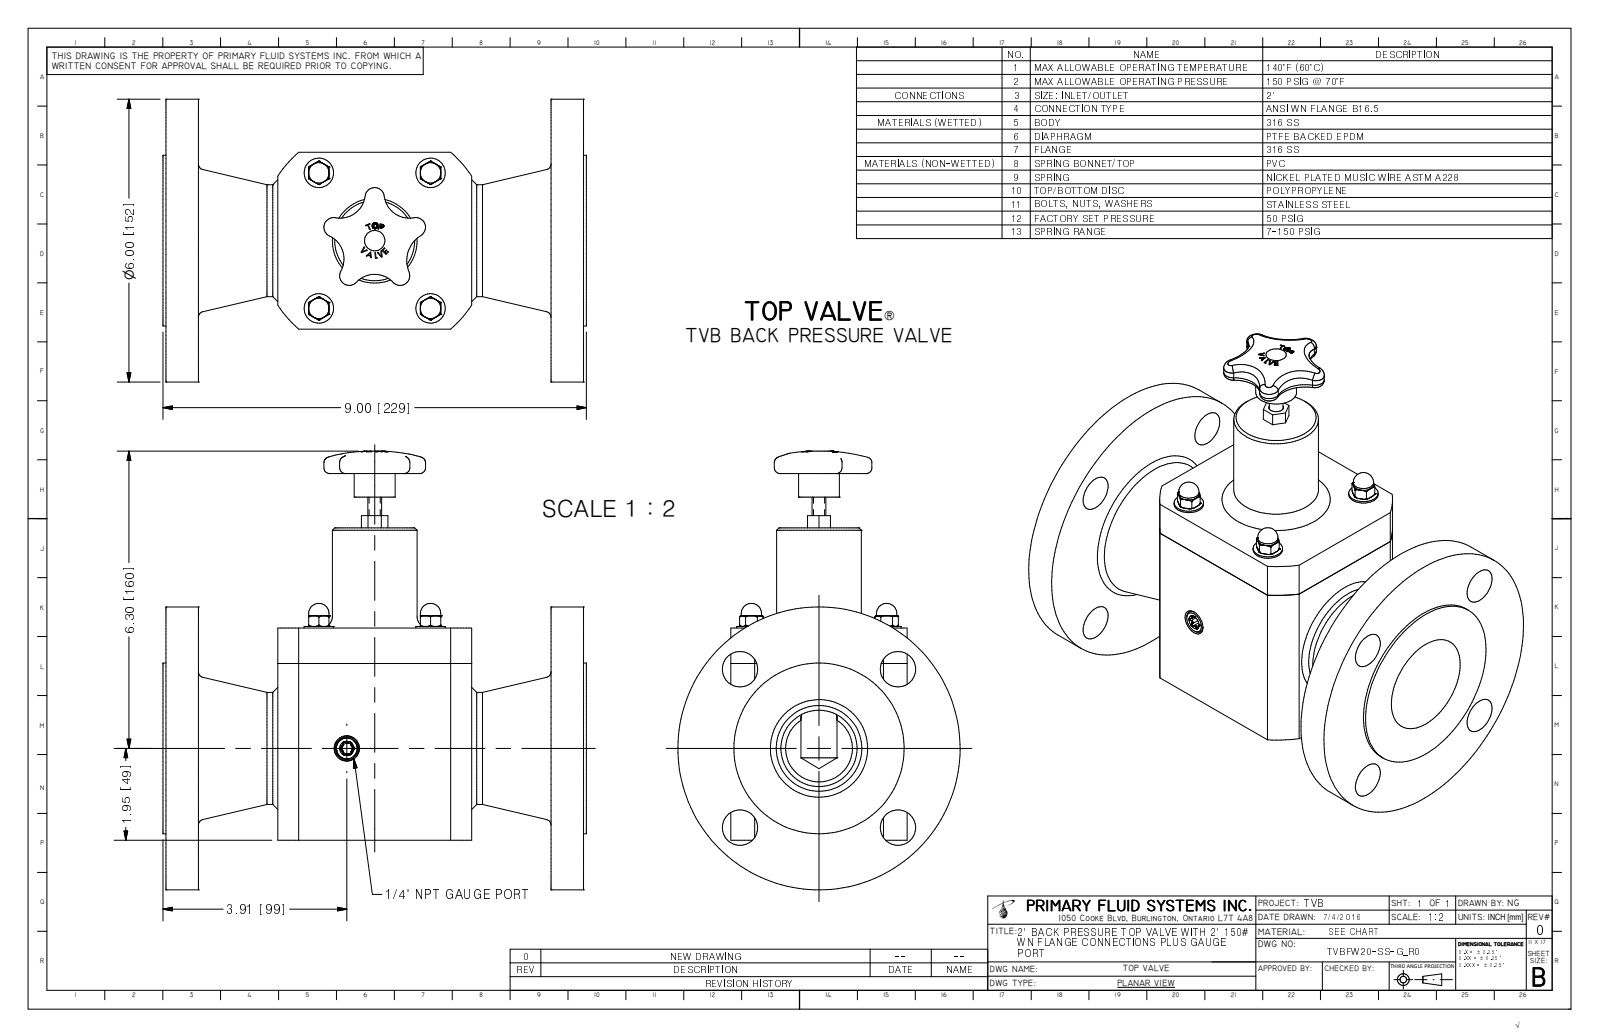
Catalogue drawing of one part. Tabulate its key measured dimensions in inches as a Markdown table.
| quantity | value |
| --- | --- |
| part name | TVBFW20-SS-G-R0 |
| STEP written by | Autodesk Inventor 2009 (AUTOMOTIVE_DESIGN) |
| units | inches |
| bodies | 1 solid, 388 faces (161 planar, 66 cylindrical, 161 other) |
| overall size | 9.304 × 9 × 6 |
| volume | 114.9 in³ |
| surface area | 306.7 in² |
| round holes (diameter × count) | 0.175 × 4, 0.75 × 4, 2.067 × 1 |
| round bosses / shafts (diameter × count) | 0.625 × 4, 0.433 × 4, 0.375 × 4, 6 × 1, 3.62 × 1, 2.375 × 1, 1.8 × 1, 0.87 × 1 |
| partial cylindrical surfaces (radius × count) | 0.027 × 6, 0.085 × 5, 0.205 × 5, 0.536 × 4, 0.656 × 4, 0.219 × 1, 0.625 × 1, 0.745 × 1 |
| main face-to-face distances | 0.69, 8.185, 7.495, 8.875, 2.375, 3.75, 6.5, 1.685, 5.81, 0.063 |
| hole center spacings | 2.375, 3.359, 2.375, 2.875, 3.729, 4.75 |
